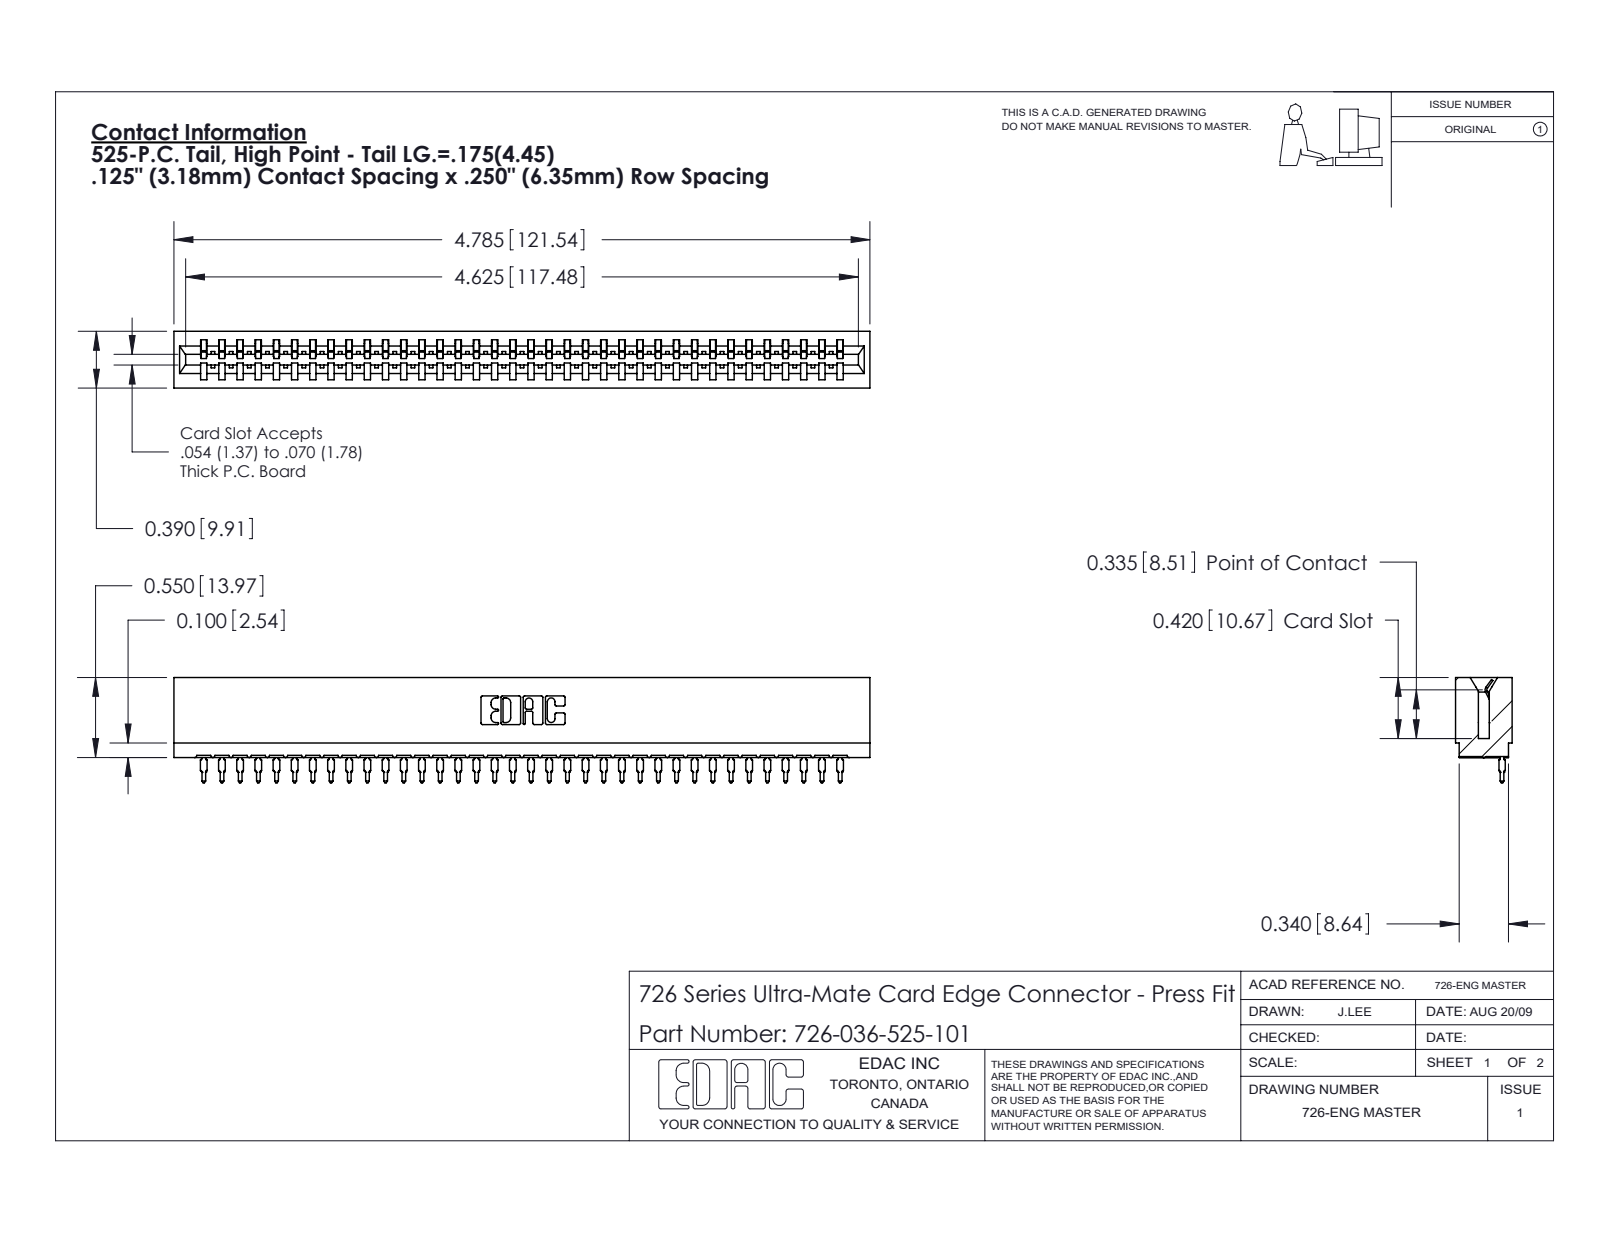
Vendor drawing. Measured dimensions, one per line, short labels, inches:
name: 726 Part_.515 Slot Depth - 01; 746-292-001_525; 726-036-525-101
written by: SolidWorks 2020 (CONFIG_CONTROL_DESIGN)
unit: in
bodies: 37 solids, 3985 faces (2323 planar, 726 cylindrical, 936 other)
size: 4.785 × 0.724 × 0.39
volume: 0.662 in³; area: 25.25 in²
rounds: 72× R0.021, 37× R0.015, 22× R0.01, 6× R0.007, 6× R0.031, 4× R0.005, 4× R0.011, 3× R0.026
face distances: 0.057, 0.333, 0.39, 0.25, 0.025, 0.307, 0.275, 0.5, 0.365, 0.032
